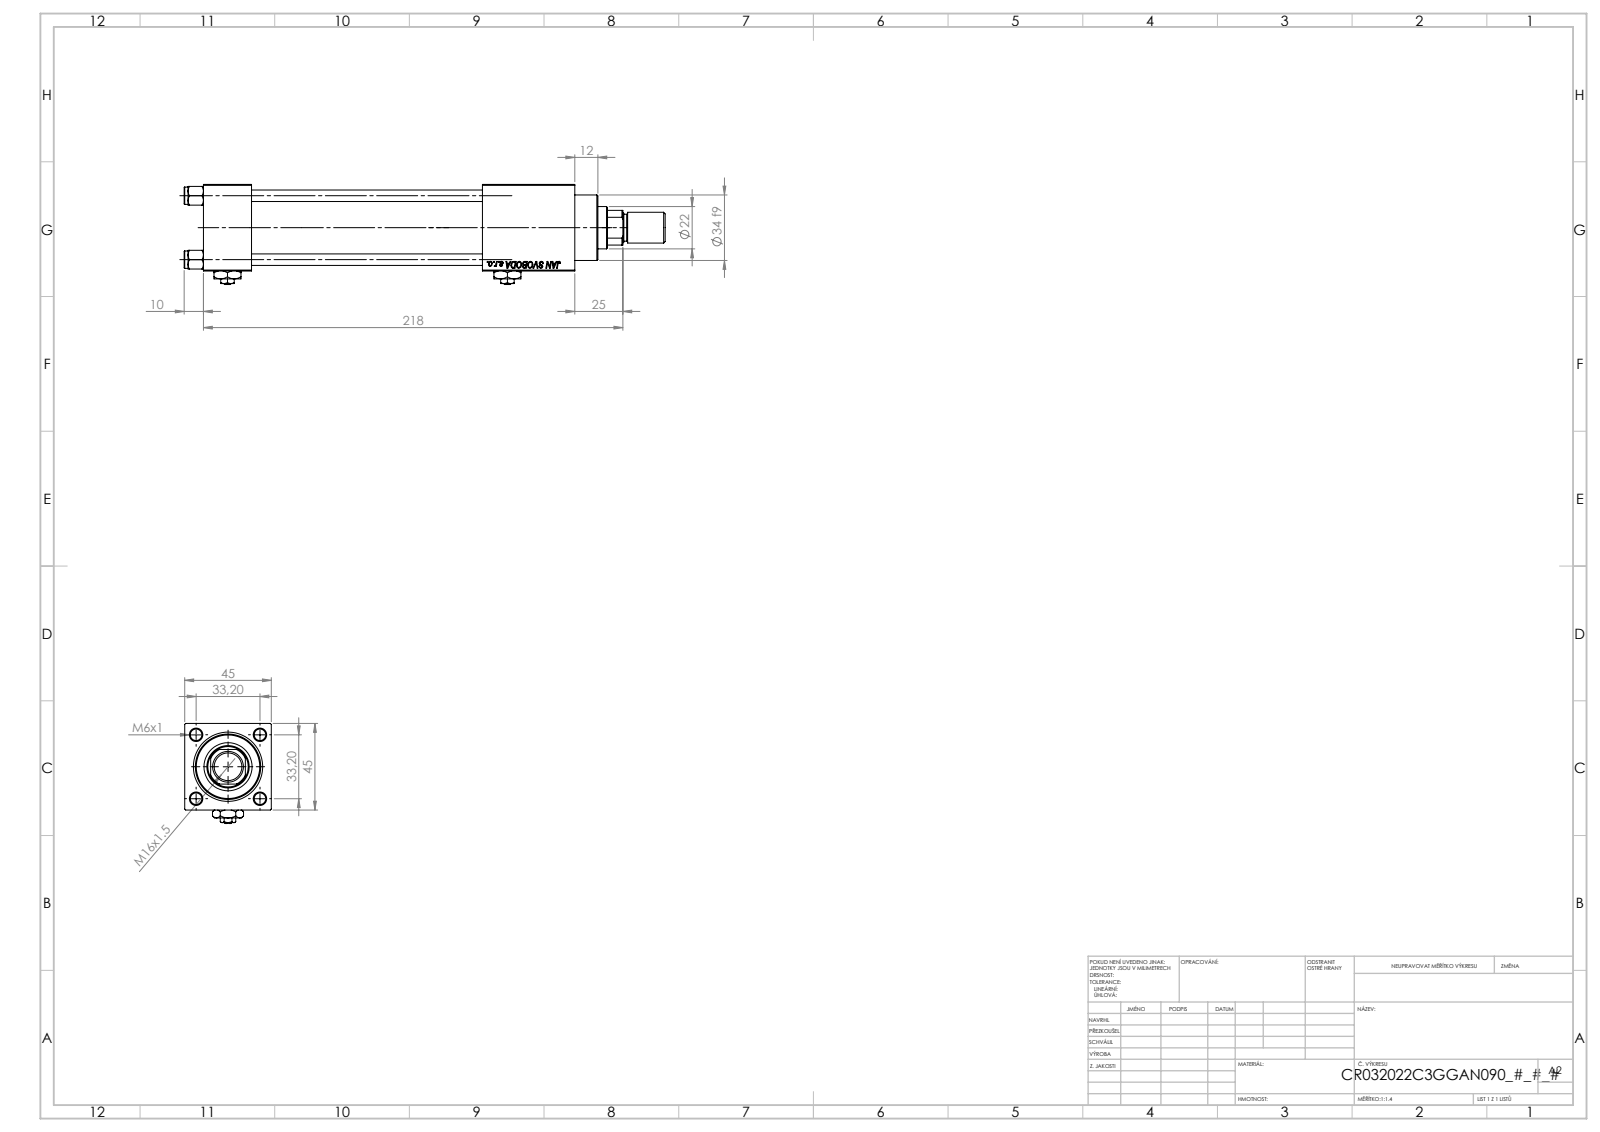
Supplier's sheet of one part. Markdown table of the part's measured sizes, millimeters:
| quantity | value |
| --- | --- |
| part name | V215CR_C_TYCINKA; V215_VC_A; Zatka_pro_OIL_PORT; NUT_M5_C (+3 more) |
| STEP written by | SolidWorks 2019 (CONFIG_CONTROL_DESIGN) |
| units | millimeters |
| bodies | 14 solids, 1262 faces (576 planar, 102 cylindrical, 584 other) |
| overall size | 250 × 52 × 45 |
| volume | 269 830 mm³ |
| surface area | 100 258 mm² |
| round holes (diameter × count) | 6 × 4, 7 × 2, 13.16 × 2, 20 × 2, 10.5 × 1, 22 × 1, 24 × 1, 25 × 1, 32 × 1, 33 × 1 |
| round bosses / shafts (diameter × count) | 9 × 4, 38 × 1, 34 × 1, 16 × 1, 14 × 1 |
| partial cylindrical surfaces (radius × count) | 10.5 × 1 |
| main face-to-face distances | 45, 25, 193, 145, 120, 168, 44.8, 48, 164.3, 139.3 |
| hole center spacings | 23.48, 33.2, 46.95, 145.5 |
